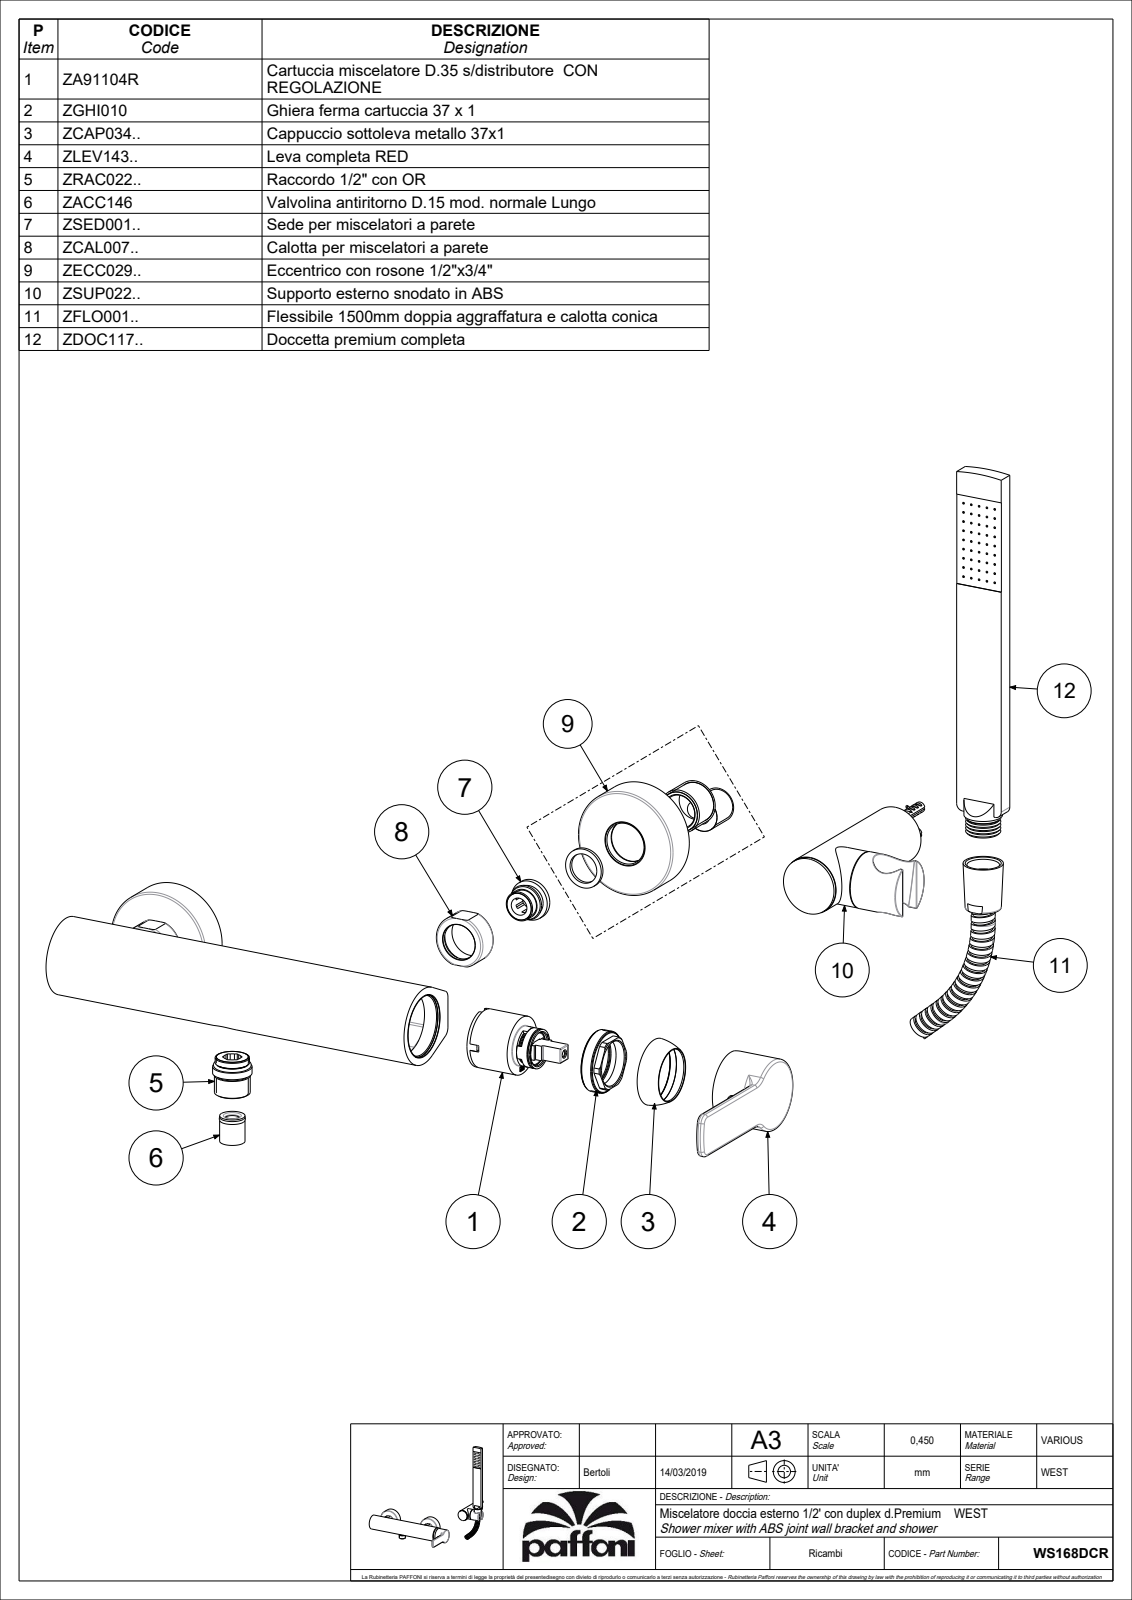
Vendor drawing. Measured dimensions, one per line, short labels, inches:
name: WS168DCR
written by: CREO PARAMETRIC BY PTC INC, 2020044 (CONFIG_CONTROL_DESIGN)
unit: in
bodies: 3 solids, 2106 faces (1109 planar, 554 cylindrical, 443 other)
size: 16.526 × 14.683 × 5.827
volume: 23.66 in³; area: 368.1 in²
holes: 3× ⌀0.276, 2× ⌀0.13, 2× ⌀0.138, 2× ⌀0.157, 2× ⌀0.413, 2× ⌀0.63, 2× ⌀0.709, 2× ⌀0.85, 2× ⌀0.965, 2× ⌀0.984, 2× ⌀1.142, 2× ⌀2.453
bosses: 11× ⌀0.079, 2× ⌀2.5, 2× ⌀1.063, 2× ⌀0.945, 2× ⌀0.906, 2× ⌀0.697, 1× ⌀1.693, 1× ⌀1.398
rounds: 66× R0.02, 48× R0.059, 11× R0.006, 10× R0.012, 8× R0.197, 4× R0.079, 4× R0.205, 2× R0.039
face distances: 0.146, 0.394, 1.988, 0.024, 2.012, 2.406, 2.382, 1.37, 1.173, 1.398
hole spacings: 0.278, 0.339, 0.449, 0.157, 0.236, 0.394, 0.492, 0.551
